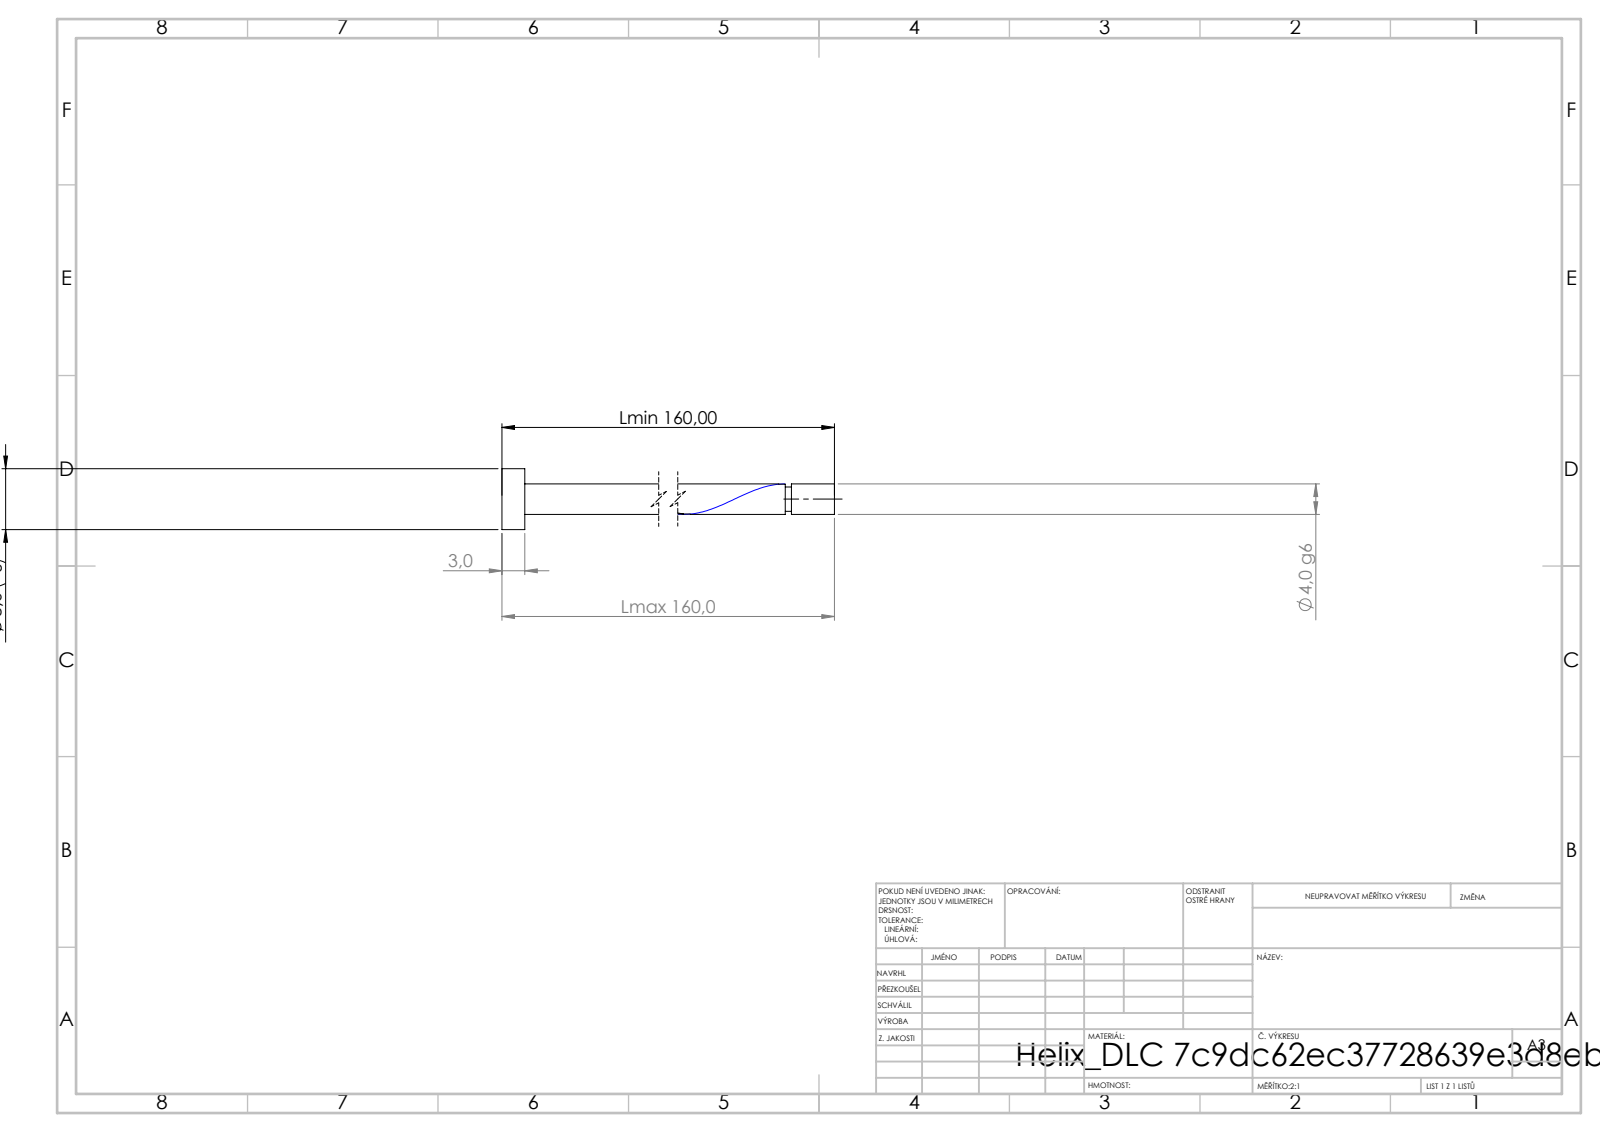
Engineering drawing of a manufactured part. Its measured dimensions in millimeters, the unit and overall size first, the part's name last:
Units: millimetres
Overall size (bounding box): 160 × 8 × 8
Round bosses / shafts (diameter × count): ⌀8 ×1, ⌀4 ×1, ⌀3.2 ×1
Main face-to-face distances: 3, 160, 157, 154.35, 151.35, 5.65, 153.55, 150.55, 0.8, 6.45
Volume: 2 101 mm³ · Surface area: 2 191 mm²
Bodies: 1 solid, 21 faces (6 planar, 14 cylindrical, 1 other)
STEP written by: SolidWorks 2019 (CONFIG_CONTROL_DESIGN)
